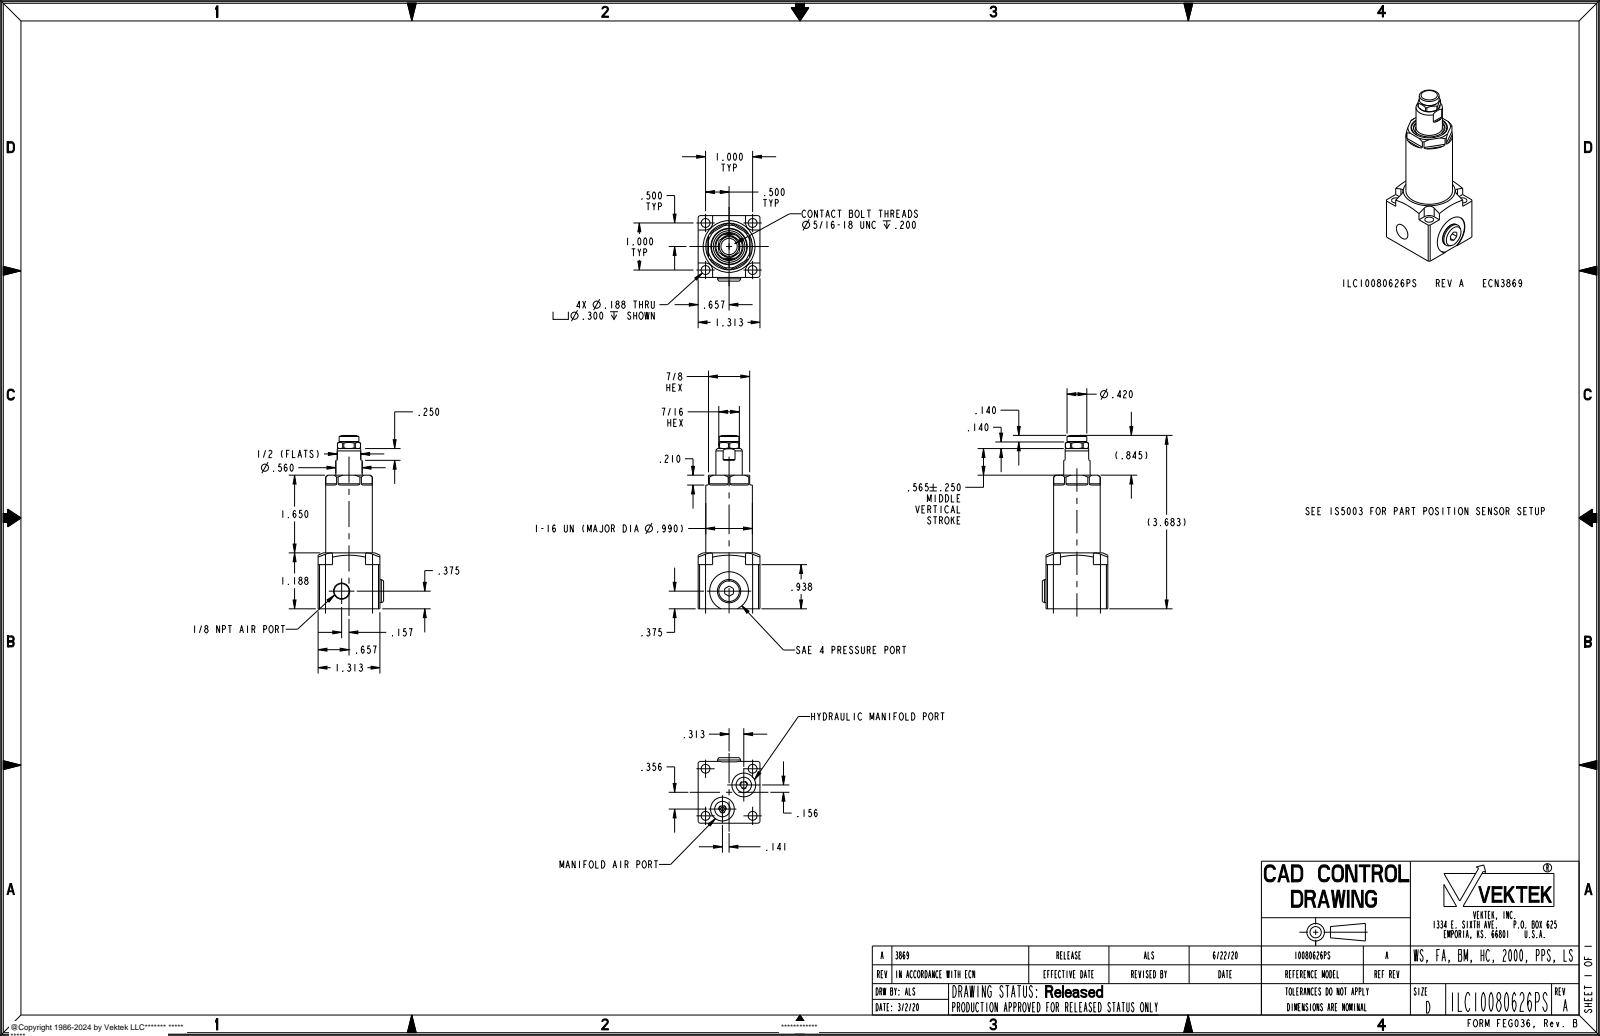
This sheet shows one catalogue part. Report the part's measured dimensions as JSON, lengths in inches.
{"part_name": "ILC10080626PS", "step_written_by": "PRO/ENGINEER BY PARAMETRIC TECHNOLOGY CORPORATION, 2013320 (CONFIG_CONTROL_DESIGN)", "units": "inches", "bodies": {"solids": 1, "faces": 185, "planar": 70, "cylindrical": 65, "other": 50}, "overall_size": [3.683, 1.391, 1.313], "volume_in3": 3.113, "surface_area_in2": 21.59, "round_holes": [[0.188, 4], [0.136, 2], [0.164, 2], [0.328, 2], [0.505, 2], [0.078, 1], [0.271, 1], [0.392, 1], [0.67, 1], [0.825, 1]], "round_bosses_or_shafts": [[0.99, 1], [0.75, 1], [0.56, 1], [0.438, 1], [0.437, 1], [0.42, 1], [0.313, 1]], "partial_cylinders_radius": [[0.027, 6], [0.15, 4], [0.018, 2], [0.245, 1]], "face_to_face_distances": [1.313, 1.313, 1.303, 0.875, 0.938, 0.219, 0.077, 0.861, 0.25, 1.188], "hole_center_spacings": [0.707, 1, 1.414, 0.349, 0.383, 0.387, 0.392, 0.657]}
